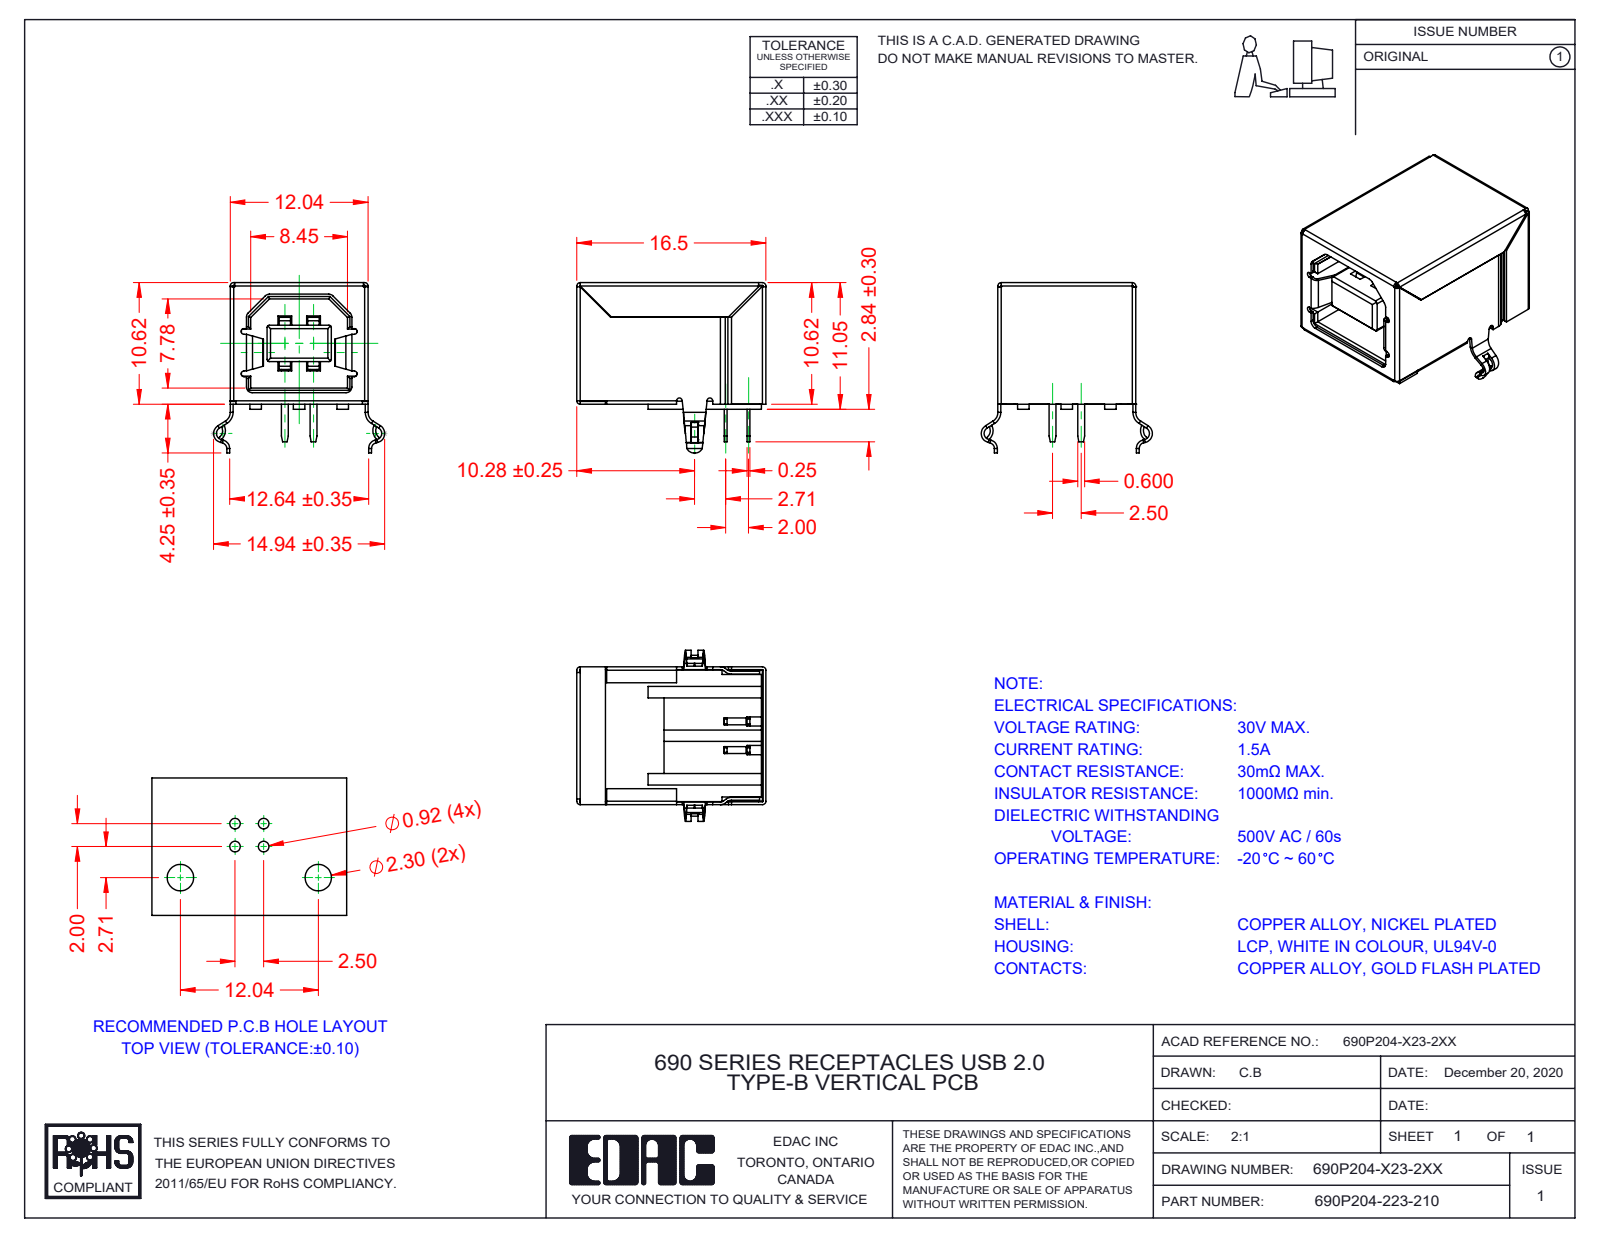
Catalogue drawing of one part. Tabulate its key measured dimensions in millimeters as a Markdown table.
| quantity | value |
| --- | --- |
| part name | SHELL 690P204-X23-2XX; INSULATOR 690P204-X23-2XX_White; CONTACT01 690P204-X23-2XX; 690P204-123-210 (+1 more) |
| STEP written by | SolidWorks 2020 (AUTOMOTIVE_DESIGN) |
| units | millimeters |
| bodies | 6 solids, 631 faces (436 planar, 167 cylindrical, 28 other) |
| overall size | 16.5 × 14.94 × 14.87 |
| volume | 1 499 mm³ |
| surface area | 3 521 mm² |
| partial cylindrical surfaces (radius × count) | 0.1 × 14, 0.3 × 13, 0.5 × 12, 0.25 × 8, 0.75 × 8, 0.55 × 6, 0.2 × 4, 0.6 × 4 |
| main face-to-face distances | 11.79, 11.77, 11.52, 10.35, 12.04, 11.54, 10.1, 10.08, 0.38, 10.37 |
